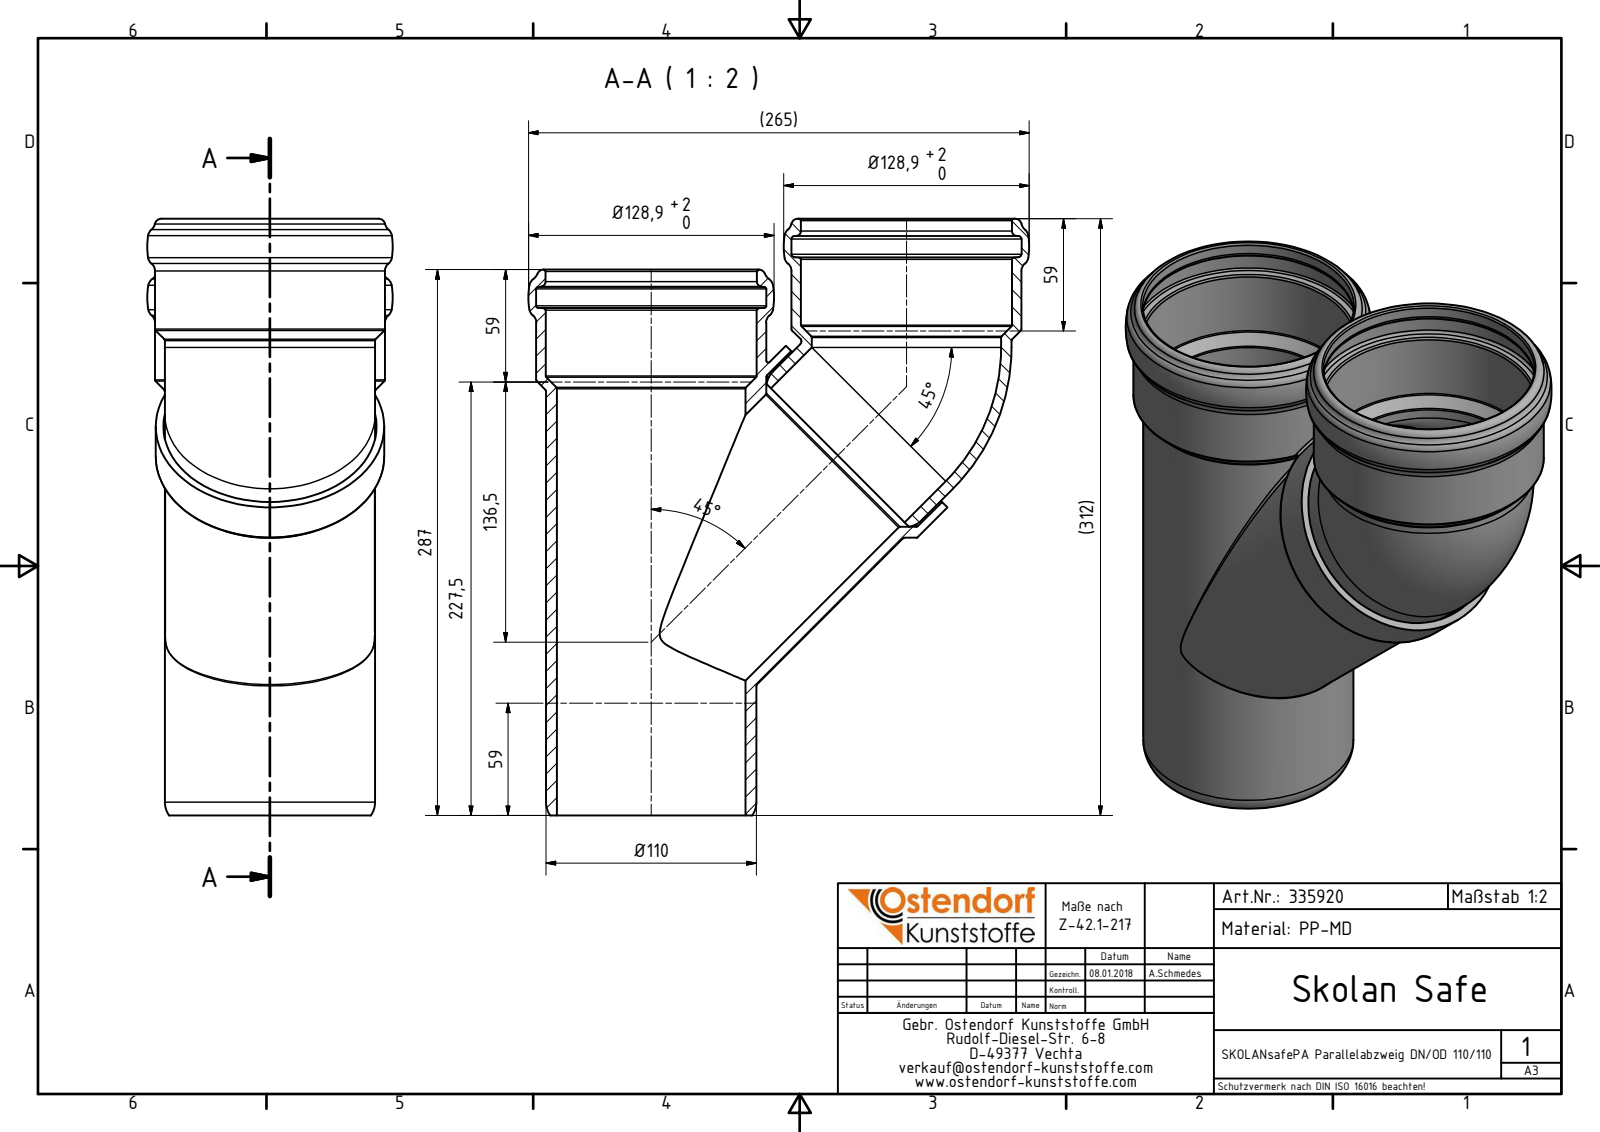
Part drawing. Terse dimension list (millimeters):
name: 335920 SKPA Parallelabzweig DN_OD 110_110 teil 1; 335920 SKPA Parallelabzweig DN_OD 110_110 teil 2; 335920 SKOLANsafePA Parallelabzweig DN_OD 110_110 Zusammenbau
written by: Autodesk Inventor 2016 (AUTOMOTIVE_DESIGN)
unit: mm
bodies: 2 solids, 96 faces (3 planar, 18 cylindrical, 75 other)
size: 313.26 × 262.96 × 128.9
volume: 909 791 mm³; area: 349 926 mm²
holes: 2× ⌀99.4, 2× ⌀110.8, 2× ⌀120.9, 1× ⌀98.6, 1× ⌀99, 1× ⌀111, 1× ⌀112
bosses: 3× ⌀110.4, 2× ⌀120.8, 1× ⌀120, 1× ⌀110
face distances: 21.41
hole spacings: 134.06
